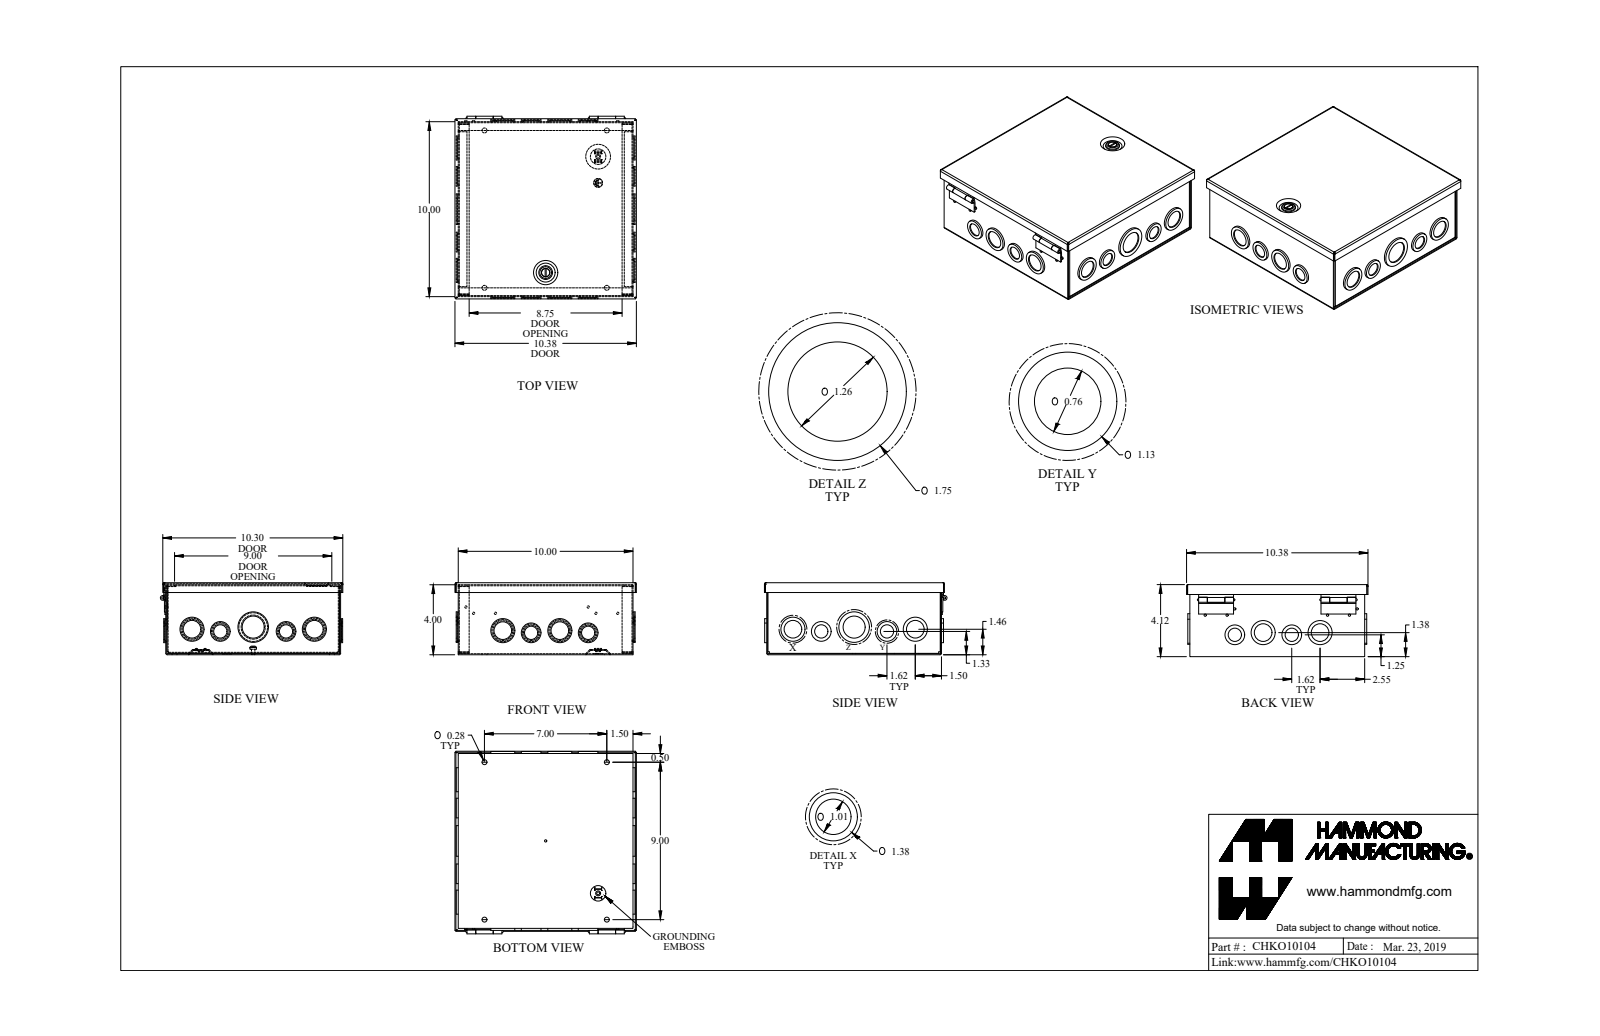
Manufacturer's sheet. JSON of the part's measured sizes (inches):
{"part_name": "CHKO10104_Default", "step_written_by": "SolidWorks 2019 (CONFIG_CONTROL_DESIGN)", "units": "inches", "bodies": {"solids": 12, "faces": 703, "planar": 344, "cylindrical": 316, "other": 43}, "overall_size": [10.443, 10.38, 4.118], "volume_in3": 25.38, "surface_area_in2": 894.1, "round_holes": [[1.011, 8], [1.261, 5], [0.281, 4], [0.761, 4], [0.125, 1], [0.17, 1], [0.319, 1], [0.476, 1], [0.5, 1], [1.636, 1]], "round_bosses_or_shafts": [[0.131, 8], [1.125, 6], [1.375, 4], [0.875, 4], [1.375, 3], [1.125, 2], [0.875, 2], [1.75, 1]], "partial_cylinders_radius": [[0.029, 16], [0.086, 16], [0.057, 8], [0.012, 4], [0.1, 4], [0.036, 2], [0.079, 2], [0.25, 2]], "face_to_face_distances": [0.057, 4.061, 9.943, 4.118, 4.004, 10, 9.886, 3.943, 0.118, 0.08], "hole_center_spacings": [1.625, 7, 1.896, 3.26, 3.502, 5.381, 9, 11.402]}
